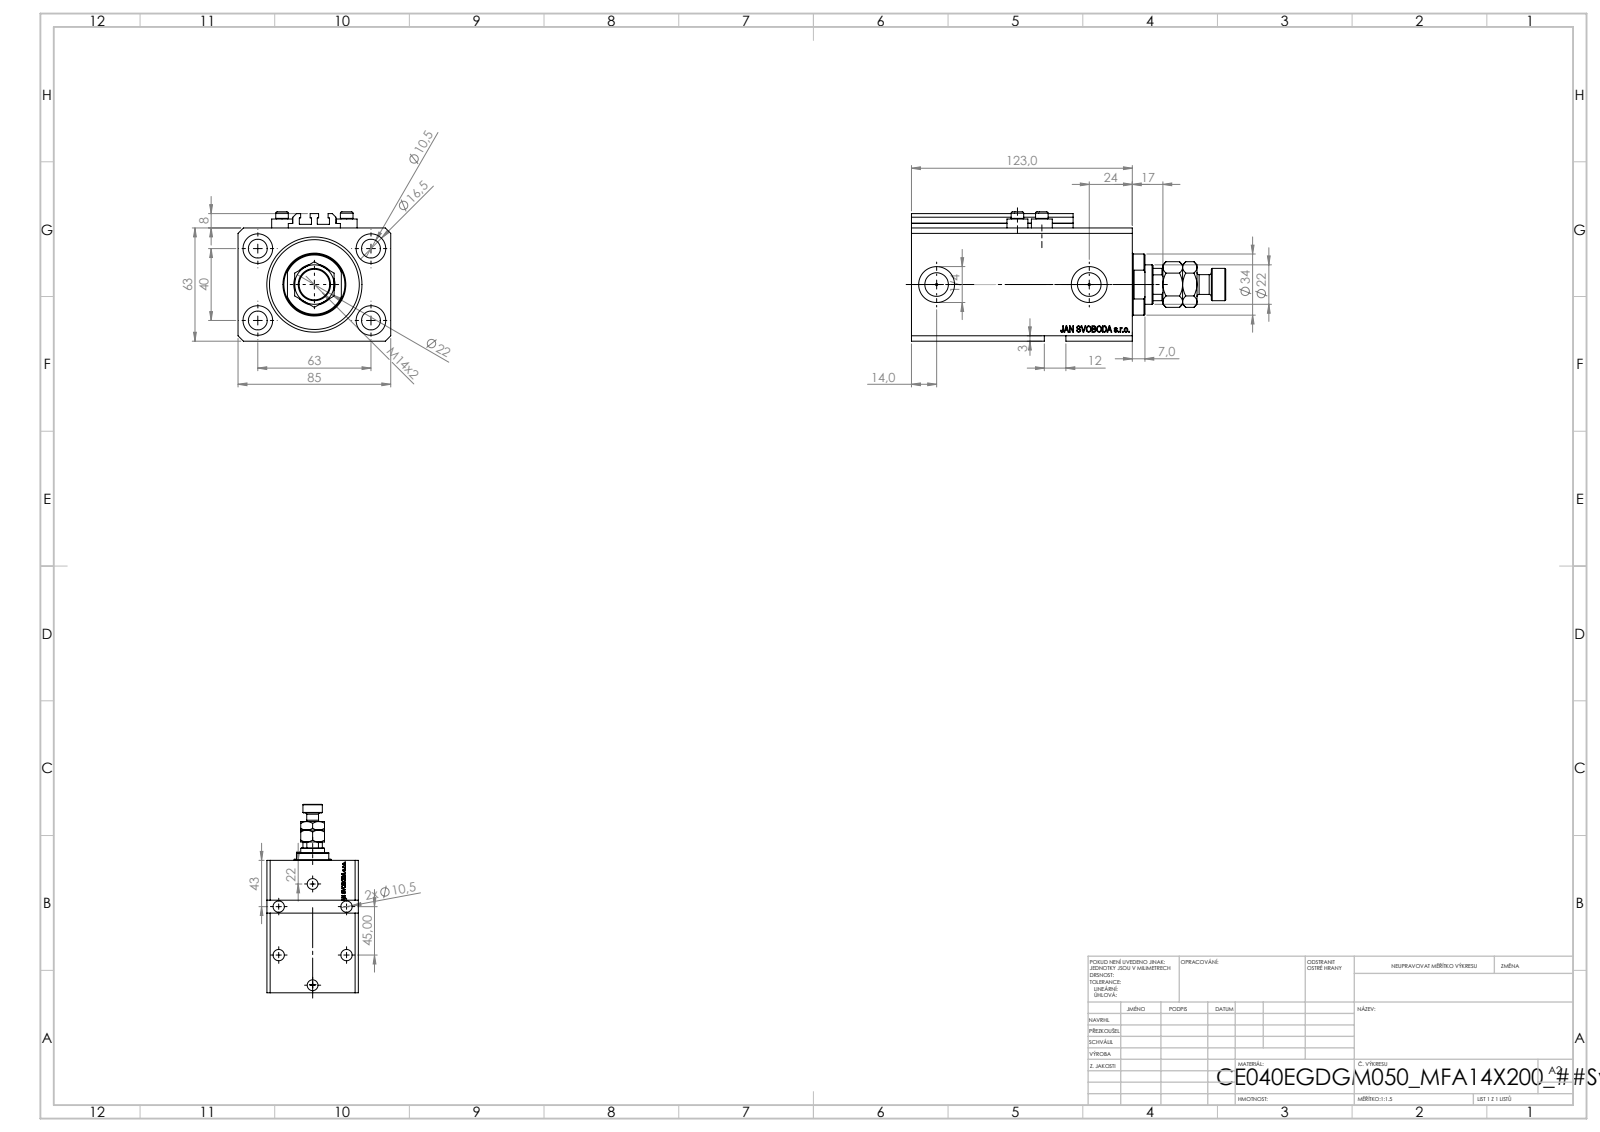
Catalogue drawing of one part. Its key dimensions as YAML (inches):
part_name: "V250CE_E_Body; V250CE_C_VCP; V250CE_VC_E; MFA (+1 more)"
step_written_by: "SolidWorks 2019 (CONFIG_CONTROL_DESIGN)"
units: inches
bodies: {solids: 9, faces: 1175, planar: 555, cylindrical: 162, other: 458}
overall_size: [6.89, 3.346, 2.835]
volume: 34.4
surface_area: 191.8
round_holes:
  - {diameter: 0.413, count: 8}
  - {diameter: 0.049, count: 4}
  - {diameter: 0.157, count: 4}
  - {diameter: 0.65, count: 4}
  - {diameter: 0.394, count: 2}
  - {diameter: 0.518, count: 2}
  - {diameter: 0.787, count: 2}
  - {diameter: 0.492, count: 1}
  - {diameter: 0.866, count: 1}
  - {diameter: 1.575, count: 1}
  - {diameter: 2.087, count: 1}
round_bosses_or_shafts:
  - {diameter: 0.457, count: 4}
  - {diameter: 0.276, count: 4}
  - {diameter: 1.339, count: 1}
  - {diameter: 0.709, count: 1}
  - {diameter: 0.433, count: 1}
partial_cylinders:
  - {radius: 0.008, count: 10}
  - {radius: 0.413, count: 1}
face_to_face_distances: [2.48, 3.346, 0.669, 4.843, 4.173, 0.449, 3.724, 4.394, 0.118, 2.205]
hole_center_spacings: [1.469, 2.48, 0.535, 0.606, 0.983, 1.084, 1.324, 1.417]
